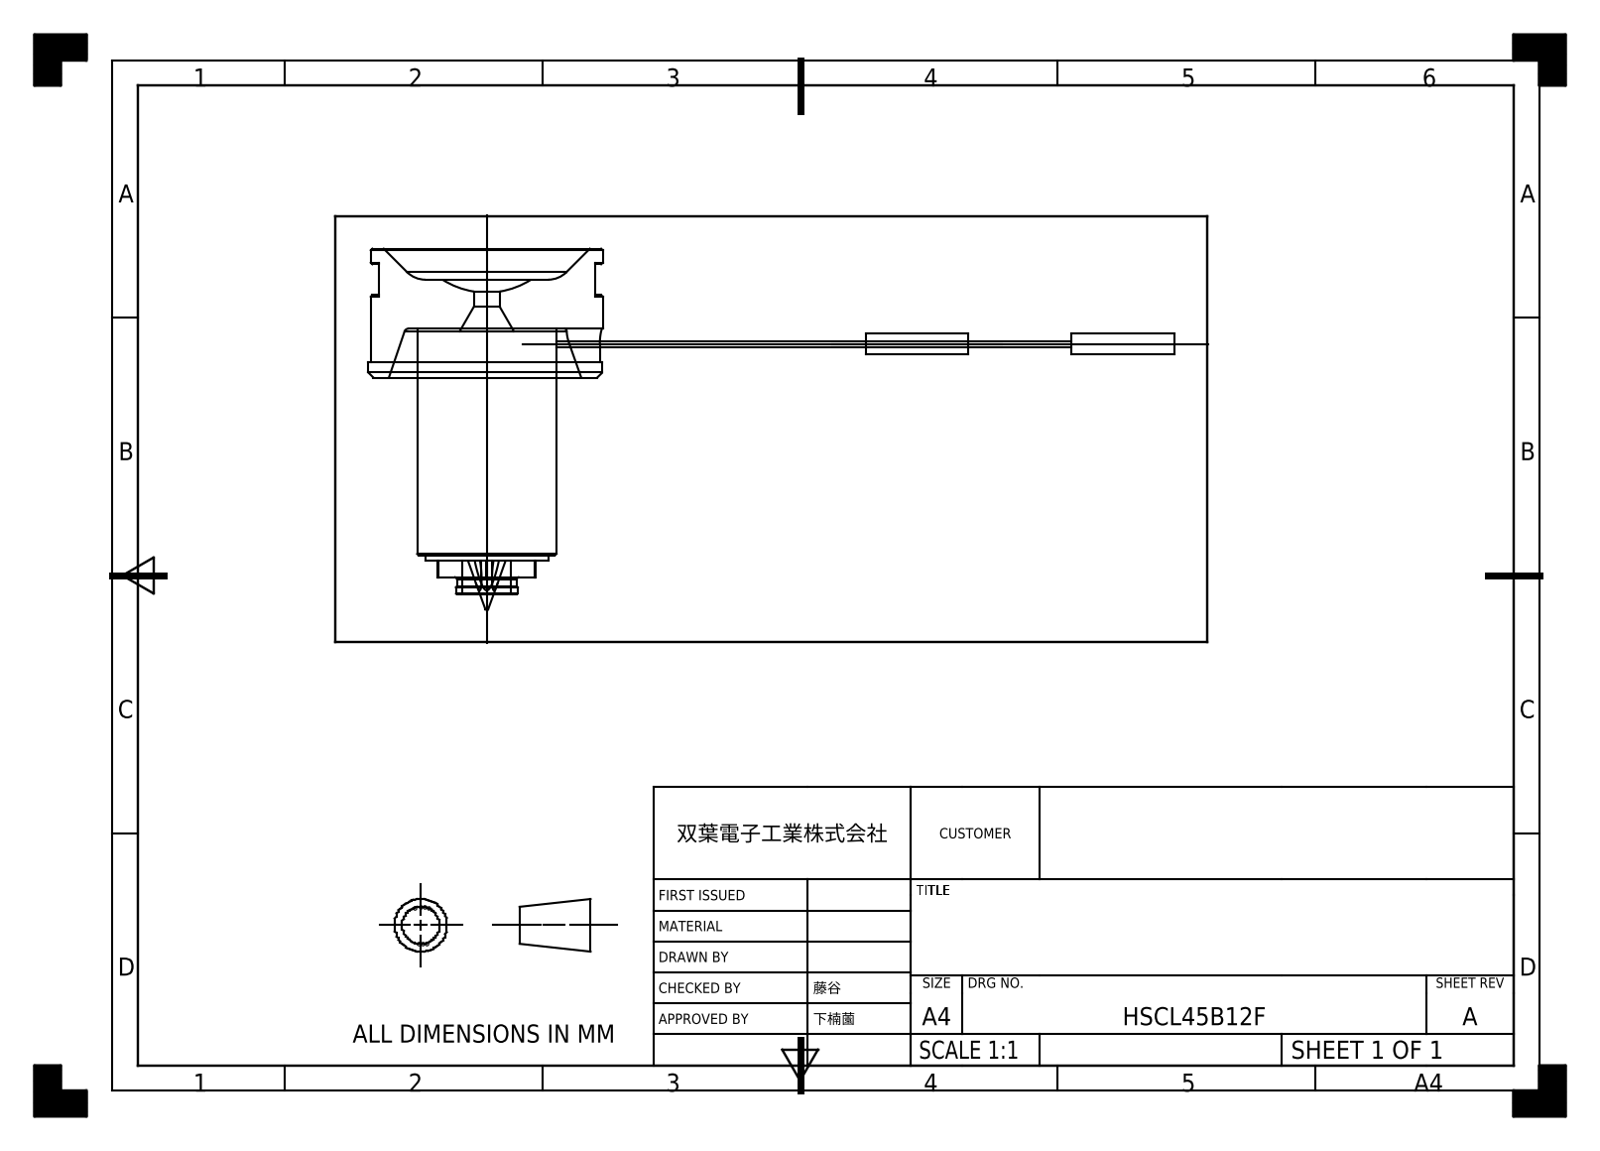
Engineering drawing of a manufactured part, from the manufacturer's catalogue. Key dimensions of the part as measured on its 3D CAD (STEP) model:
Part name (STEP PRODUCT): HSCL45B12F
STEP written by: SIEMENS PLM Software NX 2023 (AUTOMOTIVE_DESIGN)
Units: millimetres
Bodies: 5 solids, 75 faces (34 planar, 23 cylindrical, 18 other)
Overall size (bounding box): 156.5 × 70 × 46
Volume: 51 454 mm³ · Surface area: 13 546 mm²
Round holes (diameter × count): ⌀5 ×1, ⌀9.5 ×1
Round bosses / shafts (diameter × count): ⌀4 ×2, ⌀1.2 ×2, ⌀46 ×1, ⌀45 ×1, ⌀27 ×1, ⌀23.8 ×1, ⌀12 ×1, ⌀11.6 ×1
Partial cylindrical surfaces — rounded edges, fillets, slot ends (radius × count): R2.8 ×3, R3 ×2, R10.9 ×1
Main face-to-face distances: 9.5, 19, 6, 25, 45, 63.7, 57.7, 38.7, 15.5, 48.2
